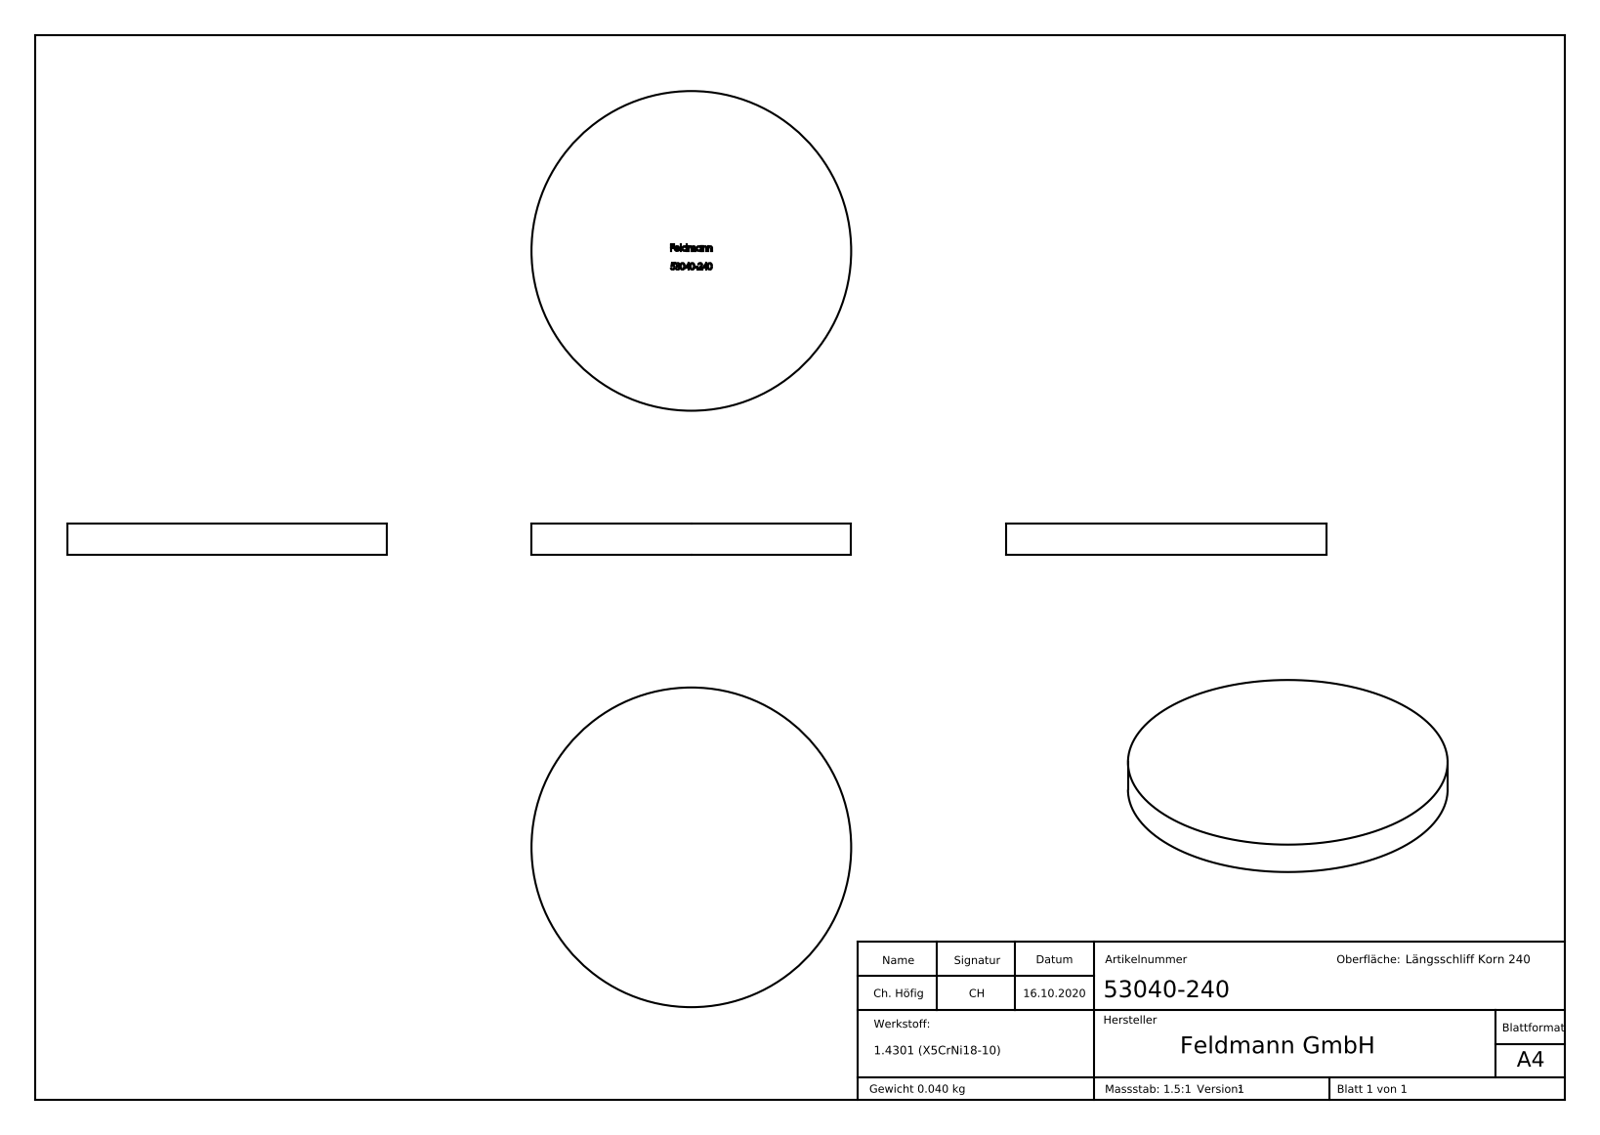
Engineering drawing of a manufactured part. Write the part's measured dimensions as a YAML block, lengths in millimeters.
part_name: "53040-240"
step_written_by: "SolidWorks 2018 (CONFIG_CONTROL_DESIGN)"
units: millimeters
bodies: {solids: 1, faces: 231, planar: 126, cylindrical: 2, other: 103}
overall_size: [40, 40, 4]
volume: 5026
surface_area: 3022
round_bosses_or_shafts:
  - {diameter: 40, count: 1}
face_to_face_distances: [4, 3.9, 2.2, 1.78, 2.18, 0.83, 2.41, 2.25, 0.99, 2.77]
